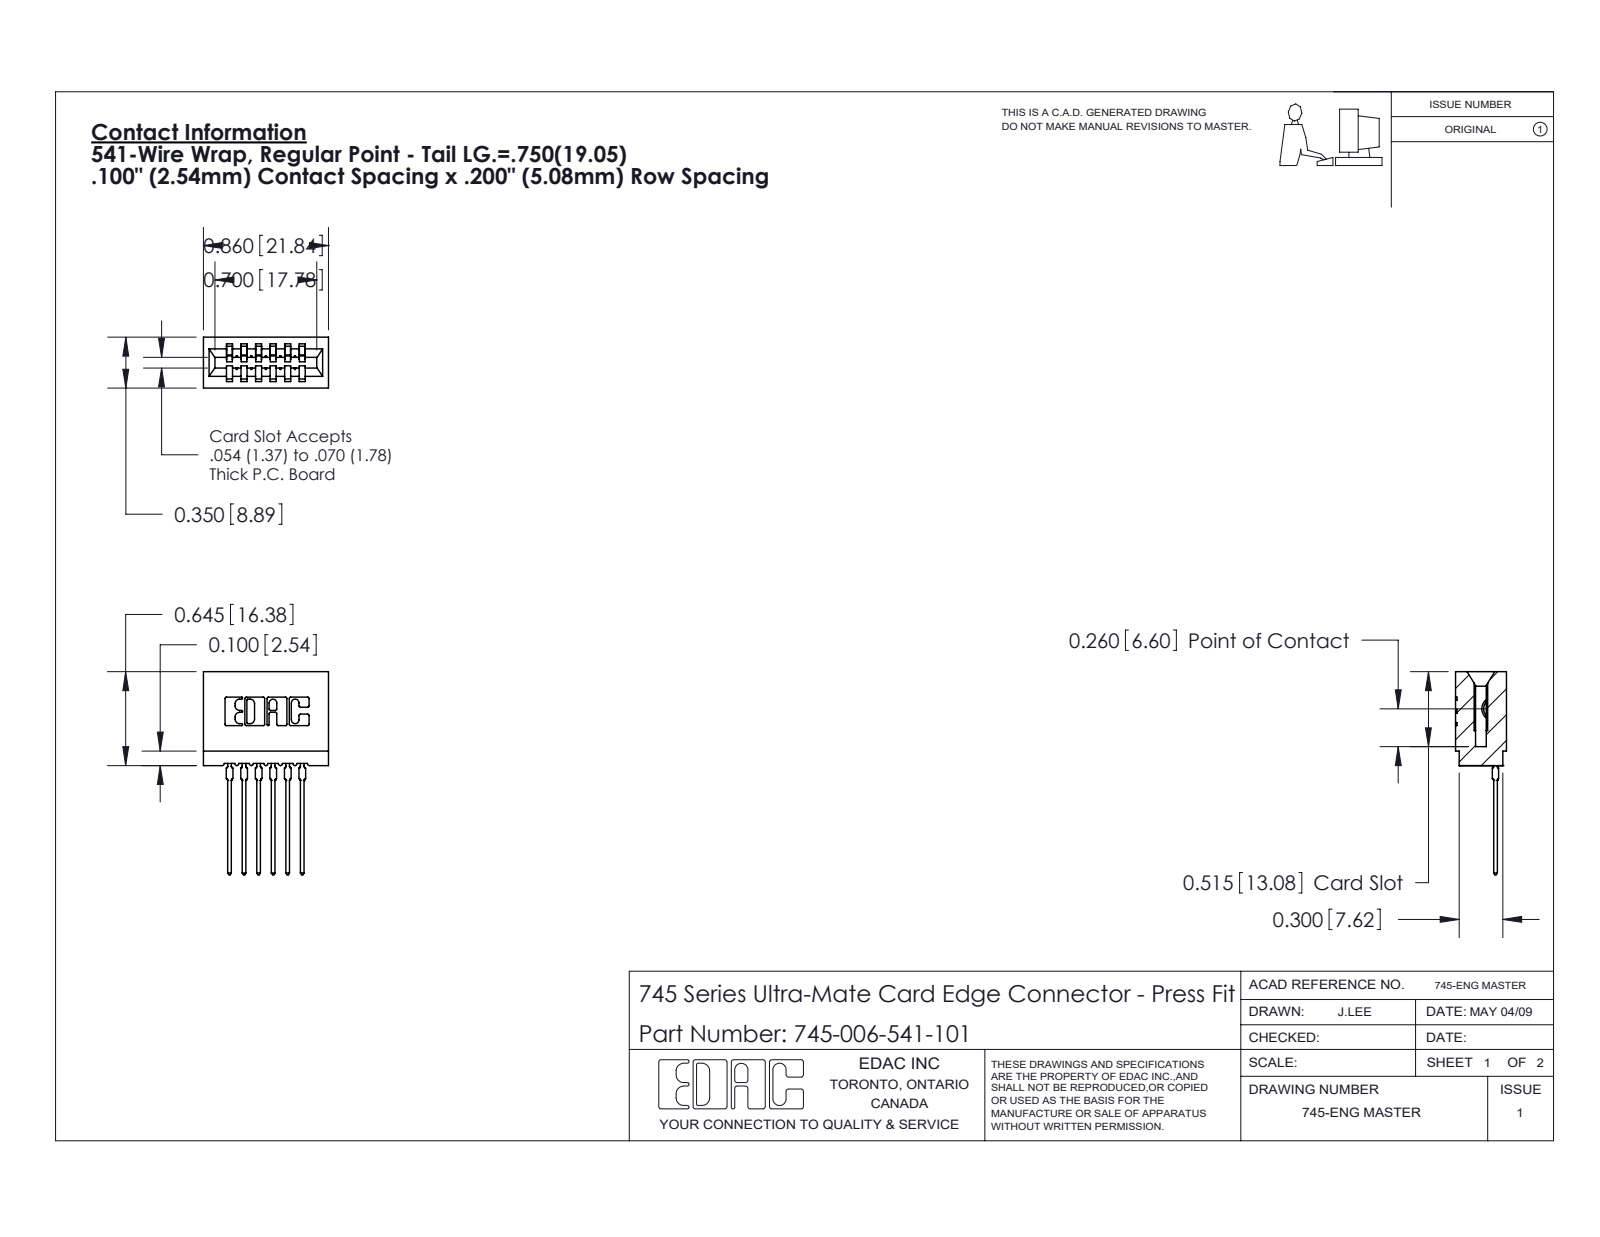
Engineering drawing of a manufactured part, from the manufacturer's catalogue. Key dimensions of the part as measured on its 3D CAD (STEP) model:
Part name (STEP PRODUCT): 745 Part_Insulator Option - 01; 745-292-001_541; 745-006-541-101
STEP written by: SolidWorks 2020 (CONFIG_CONTROL_DESIGN)
Units: inches
Bodies: 7 solids, 767 faces (457 planar, 154 cylindrical, 156 other)
Overall size (bounding box): 1.396 × 0.86 × 0.35
Volume: 0.132 in³ · Surface area: 5.307 in²
Partial cylindrical surfaces — rounded edges, fillets, slot ends (radius × count): R0.01 ×22, R0.015 ×12, R0.021 ×12, R0.007 ×6, R0.031 ×6, R0.005 ×4, R0.011 ×4, R0.026 ×3
Main face-to-face distances: 0.1, 0.2, 0.3, 0.042, 0.142, 0.058, 0.242, 0.4, 0.158, 0.35
